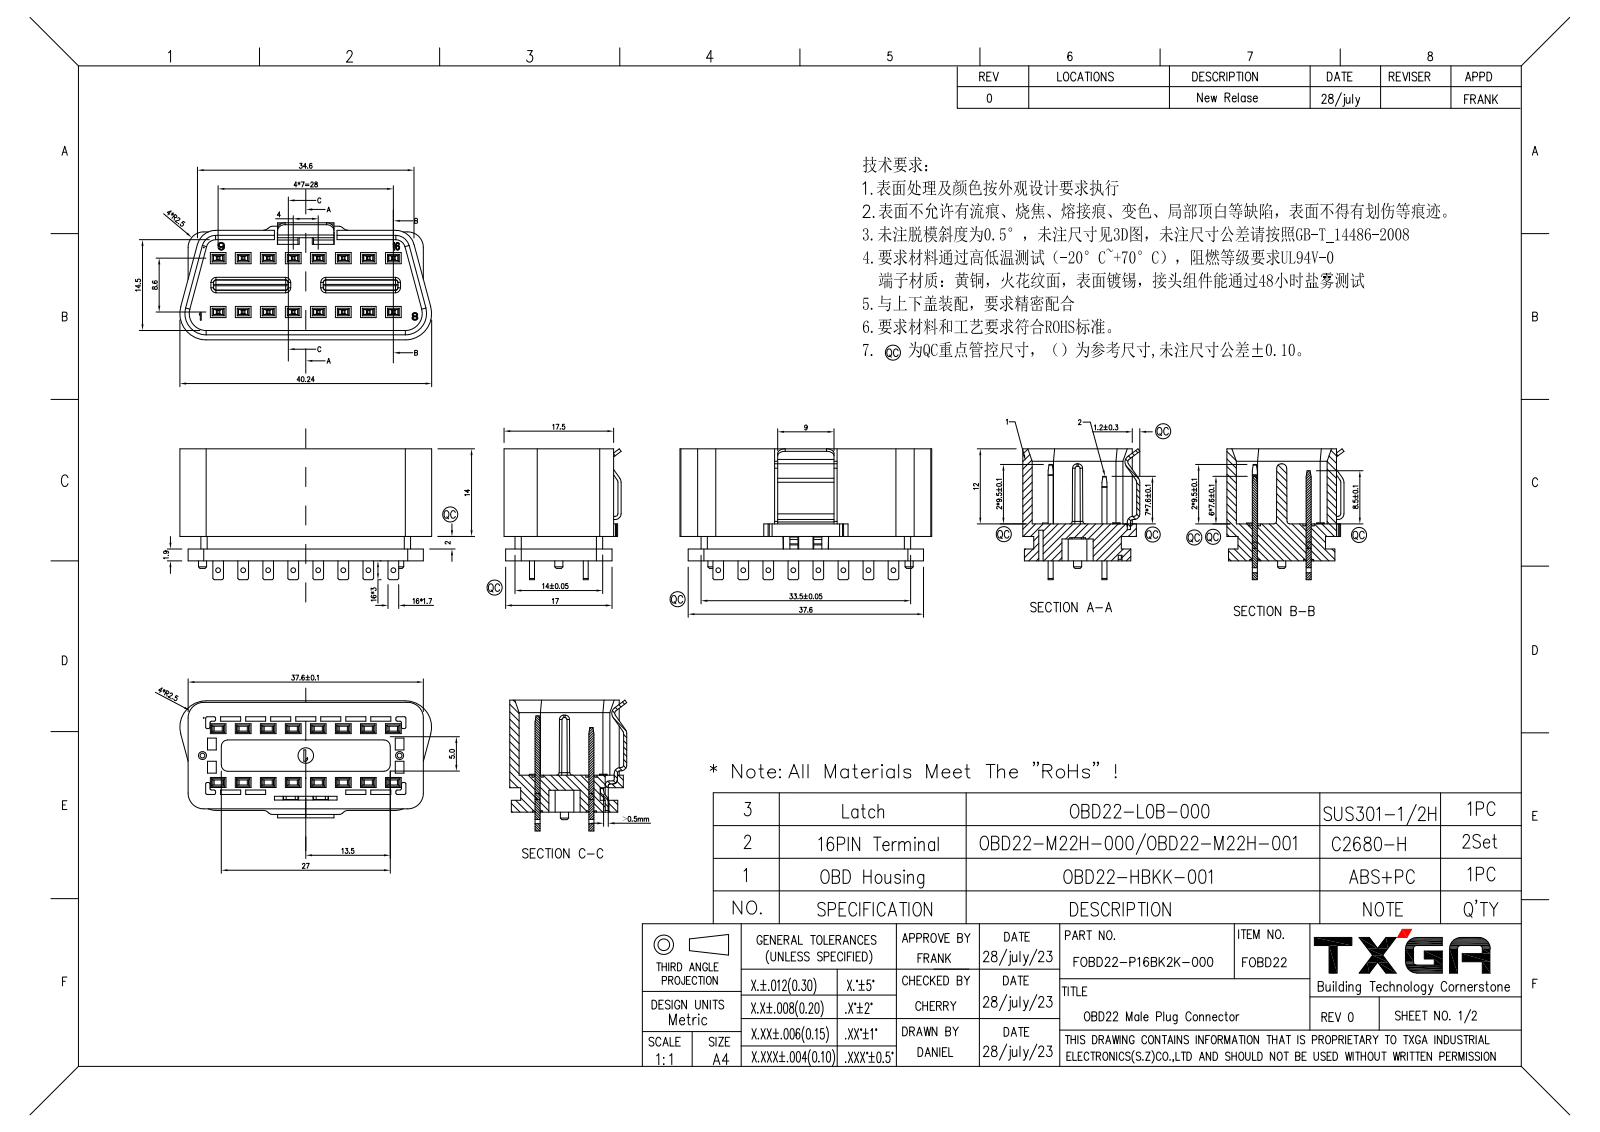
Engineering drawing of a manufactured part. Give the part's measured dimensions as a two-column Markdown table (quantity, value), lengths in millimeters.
| quantity | value |
| --- | --- |
| part name | HOUSING2233819 |
| STEP written by | PRO/ENGINEER BY PARAMETRIC TECHNOLOGY CORPORATION, 2010280 (CONFIG_CONTROL_DESIGN) |
| units | millimeters |
| bodies | 1 solid, 1247 faces (1015 planar, 208 cylindrical, 24 other) |
| overall size | 40.24 × 20.9 × 18.7 |
| volume | 4 938 mm³ |
| surface area | 7 030 mm² |
| round holes (diameter × count) | 0.8 × 8, 2.5 × 1 |
| round bosses / shafts (diameter × count) | 1.3 × 2 |
| partial cylindrical surfaces (radius × count) | 0.2 × 32, 0.15 × 22, 0.3 × 22, 0.4 × 20, 1 × 12, 0.5 × 4, 0.7 × 4, 2.5 × 4 |
| main face-to-face distances | 1.5, 0.8, 16, 2.3, 2.55, 13.45, 2, 5.9, 3, 10.9 |
| hole center spacings | 4, 8, 12, 16, 20, 24, 28 |
